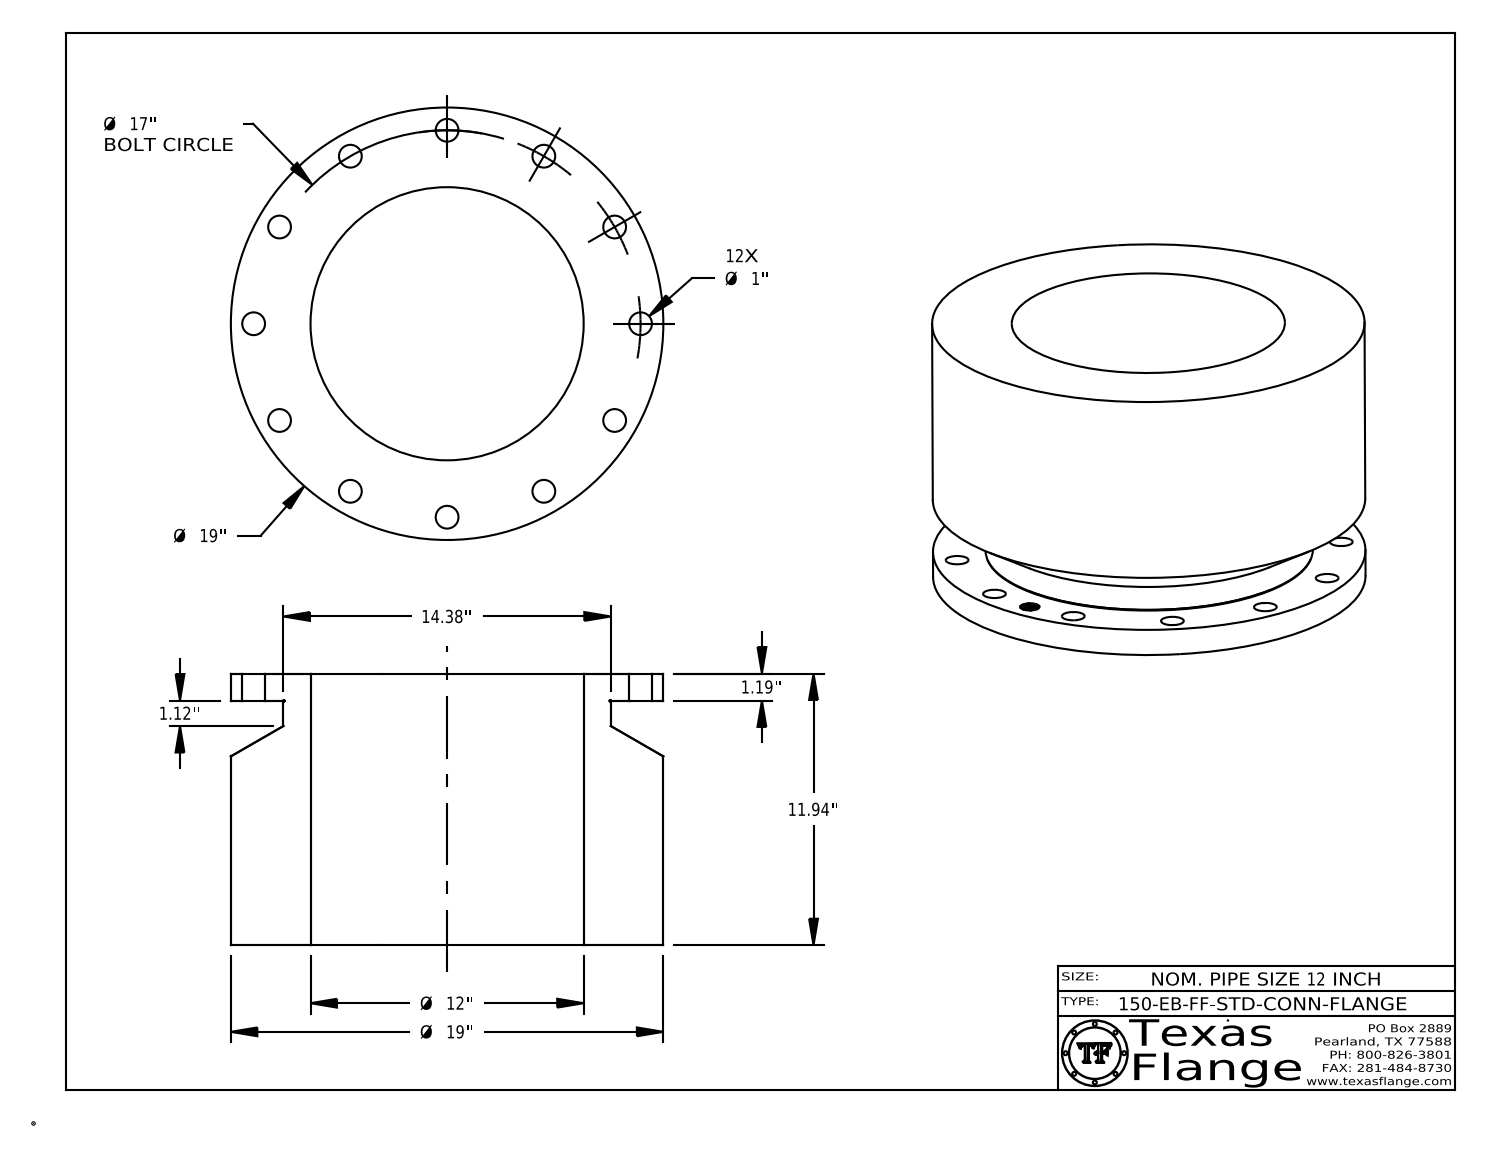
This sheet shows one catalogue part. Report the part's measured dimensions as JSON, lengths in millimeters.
{"part_name": "12-150-EB-FF-STD-CONN-FLANGE", "step_written_by": "CATIA V5 STEP AP214 (AUTOMOTIVE_DESIGN)", "units": "millimeters", "bodies": {"solids": 1, "faces": 426, "planar": 368, "cylindrical": 52, "other": 6}, "overall_size": [482.6, 482.6, 303.2], "volume_mm3": 29550000, "surface_area_mm2": 1094000, "round_holes": [[25.4, 12], [21.6, 1], [304.8, 1]], "round_bosses_or_shafts": [[1.3, 8], [482.6, 1], [365.3, 1], [17, 1]], "face_to_face_distances": [303.2, 30.1, 273.1, 30, 273.2, 6.5, 6.3, 1.2, 4.2, 5.4], "hole_center_spacings": [215.9, 417.1, 111.8, 305.3, 373.9, 111.8, 305.3, 373.9]}
